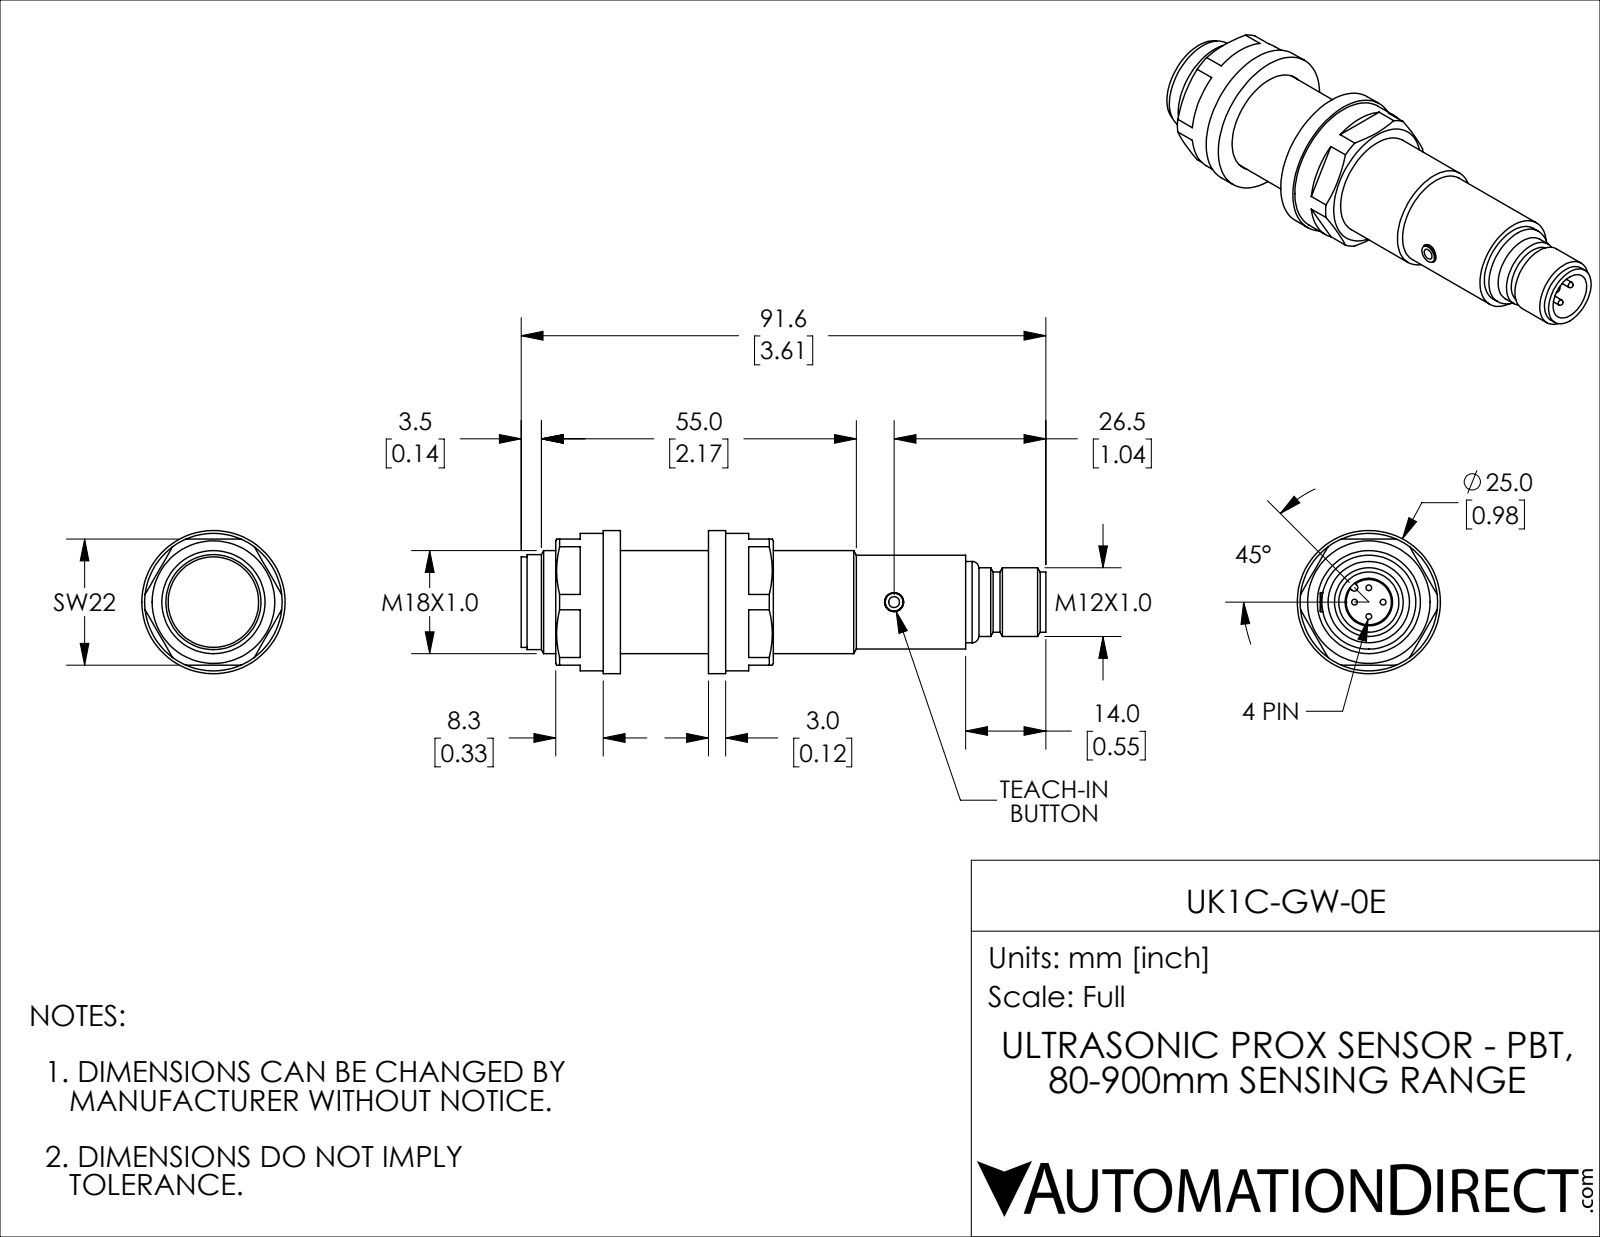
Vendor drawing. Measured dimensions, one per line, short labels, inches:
name: UK1C-GW-0E
written by: SolidWorks 2018 (AUTOMOTIVE_DESIGN)
unit: in
bodies: 6 solids, 123 faces (43 planar, 49 cylindrical, 31 other)
size: 3.606 × 0.984 × 0.984
volume: 1.477 in³; area: 16.01 in²
holes: 1× ⌀0.13, 1× ⌀0.327, 1× ⌀0.709, 1× ⌀0.717
bosses: 4× ⌀0.039, 1× ⌀0.984, 1× ⌀0.945, 1× ⌀0.654, 1× ⌀0.646, 1× ⌀0.622, 1× ⌀0.559, 1× ⌀0.472
rounds: 1× R0.024
face distances: 0.118, 0.724, 0.843, 0.606, 0.866, 0.327, 0.445, 1.051, 1.169, 0.563
